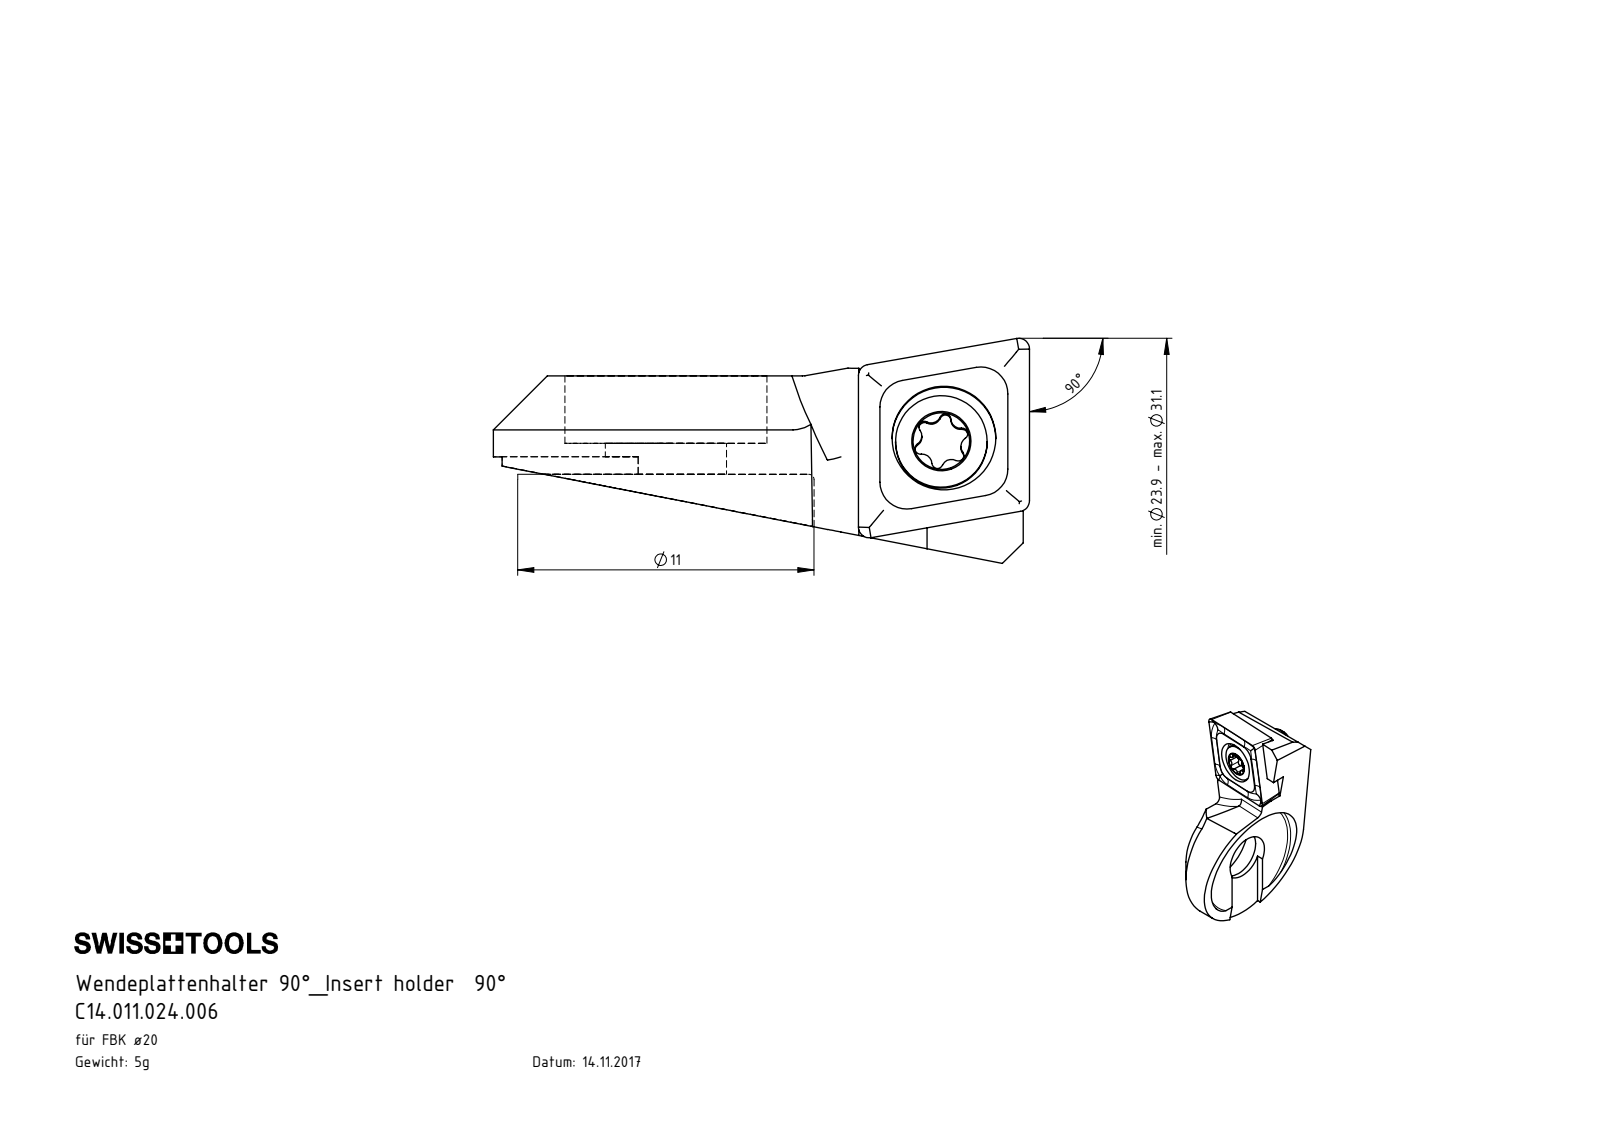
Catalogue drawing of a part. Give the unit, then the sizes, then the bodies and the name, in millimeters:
Units: millimetres
Overall size (bounding box): 19.9 × 12.8 × 8.36
Round holes (diameter × count): ⌀2.05 ×1, ⌀2.8 ×1, ⌀3.85 ×1, ⌀4.5 ×1, ⌀7.5 ×1
Round bosses / shafts (diameter × count): ⌀3.4 ×1, ⌀2.5 ×1
Partial cylindrical surfaces — rounded edges, fillets, slot ends (radius × count): R0.21 ×6, R0.36 ×5, R0.5 ×2, R5 ×2, R0.36 ×1, R5.5 ×1, R6.4 ×1, R10 ×1
Main face-to-face distances: 1.15, 2.5, 3.65, 3, 0.5, 0.65, 2.38, 2.28, 1.08, 0.98
Volume: 557 mm³ · Surface area: 853 mm²
Bodies: 3 solids, 131 faces (40 planar, 42 cylindrical, 49 other)
Part name (STEP PRODUCT): C14.011.024.006; WCA-ER2.001.006_A; CCMT060204; F20-WCA.001.005_D_fertigbearbeitet
STEP written by: SolidWorks 2017 (CONFIG_CONTROL_DESIGN)
